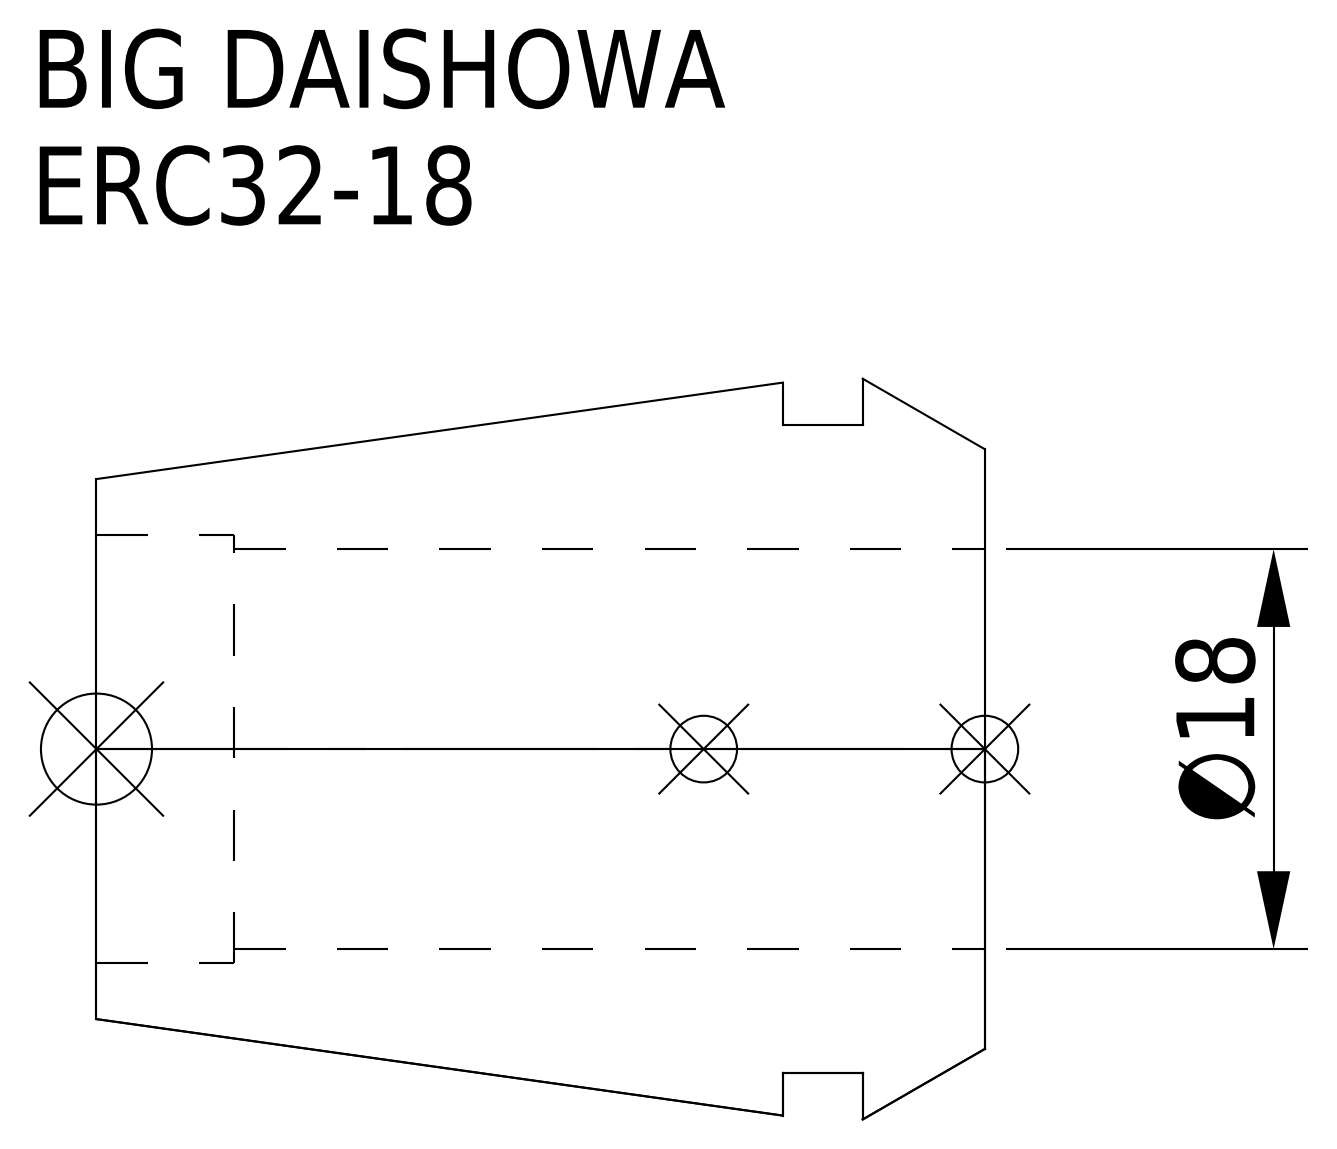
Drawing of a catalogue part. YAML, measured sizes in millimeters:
part_name: "ERC32-18"
step_written_by: "CREO PARAMETRIC BY PTC INC, 2016380 (AUTOMOTIVE_DESIGN)"
units: millimeters
bodies: {solids: 1, faces: 15, planar: 5, cylindrical: 6, other: 4}
overall_size: [40, 33.35, 33.35]
volume: 16027
surface_area: 6946
round_holes:
  - {diameter: 18, count: 1}
  - {diameter: 19.3, count: 1}
round_bosses_or_shafts:
  - {diameter: 29.2, count: 1}
face_to_face_distances: [5.5, 9.1, 3.6, 40, 34.5, 30.9, 33.8, 28.3, 24.7, 6.2]
